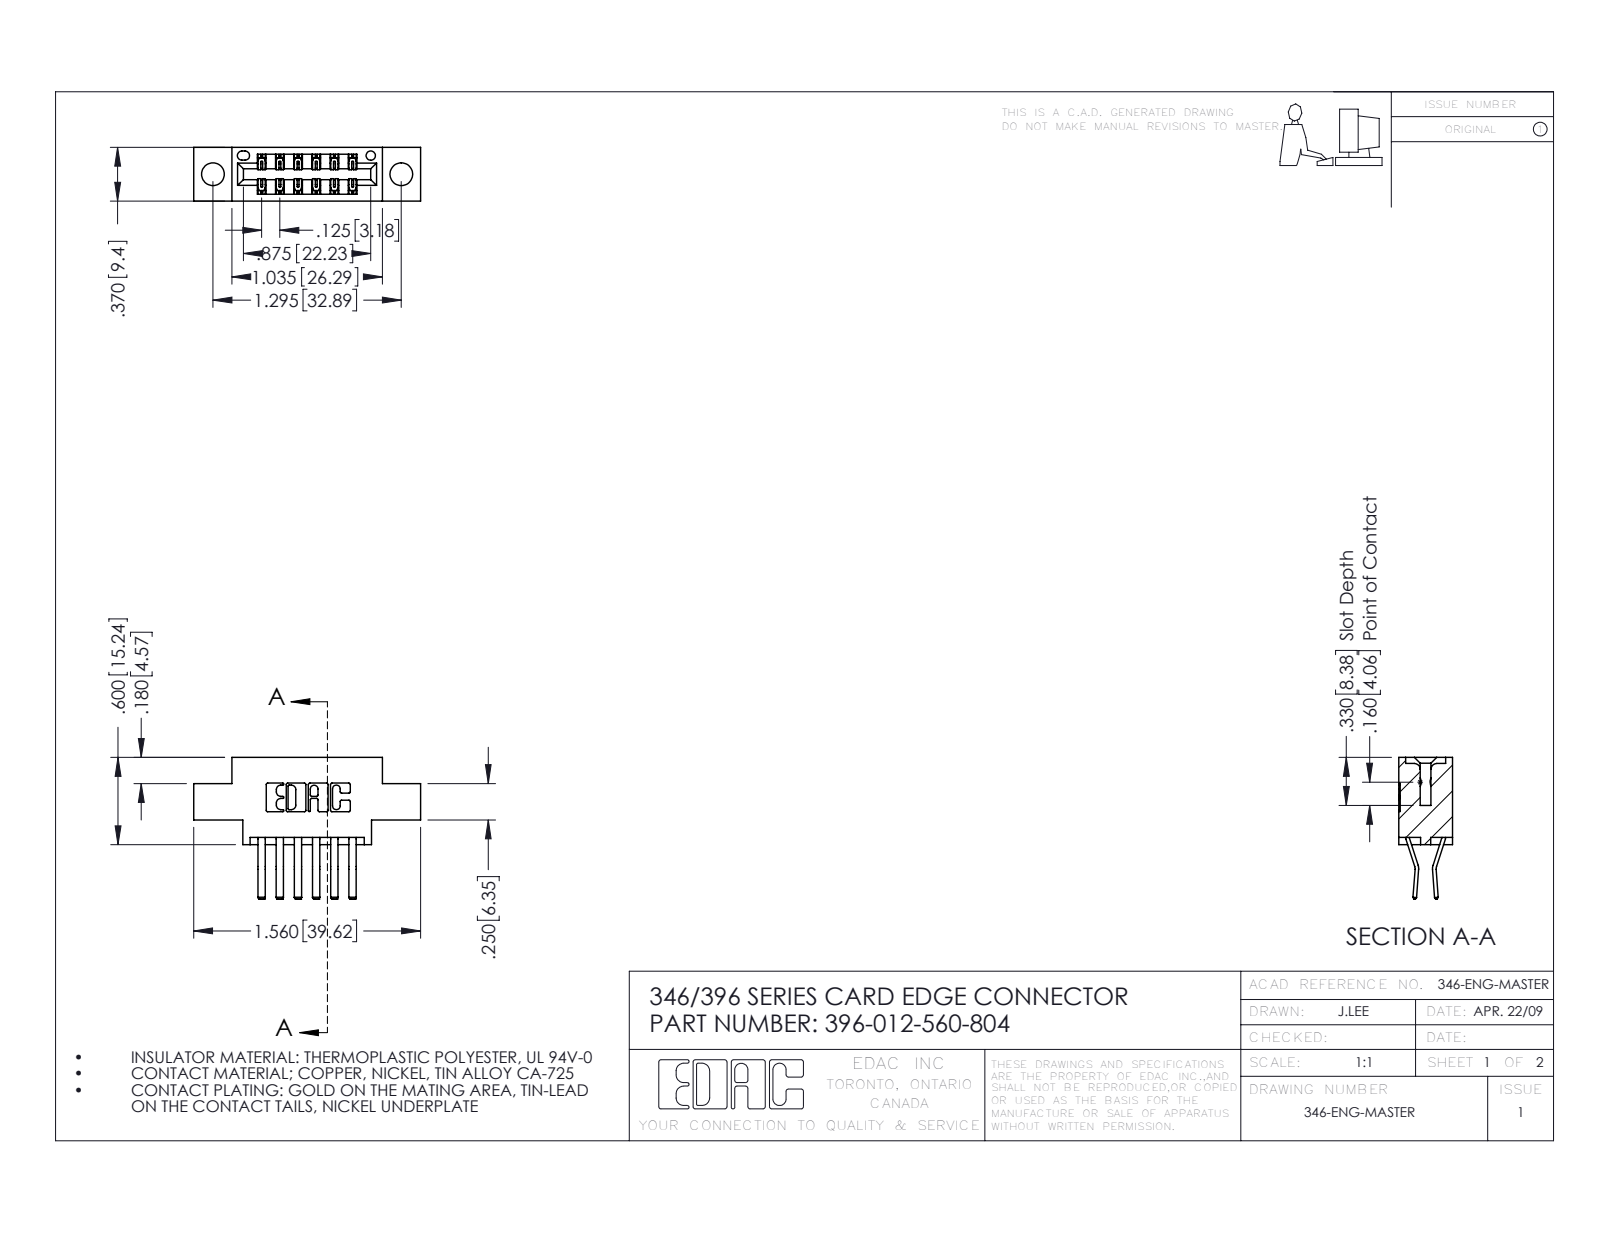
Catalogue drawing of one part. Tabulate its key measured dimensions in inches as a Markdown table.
| quantity | value |
| --- | --- |
| part name | 346 Part_0.170 Offset - 0.156 Dia-TH; 345-292-001_560 Tail; 396-012-560-804 |
| STEP written by | SolidWorks 2016 (CONFIG_CONTROL_DESIGN) |
| units | inches |
| bodies | 13 solids, 774 faces (500 planar, 274 cylindrical, 0 other) |
| overall size | 1.56 × 0.975 × 0.37 |
| volume | 0.209 in³ |
| surface area | 6.725 in² |
| round holes (diameter × count) | 0.156 × 2, 0.064 × 1 |
| partial cylindrical surfaces (radius × count) | 0.01 × 22, 0.006 × 18, 0.007 × 6, 0.031 × 6, 0.026 × 3, 0.01 × 2, 0.014 × 2, 0.022 × 2 |
| main face-to-face distances | 0.25, 0.37, 0.048, 0.322, 0.025, 0.148, 0.222, 0.1, 0.174, 0.072 |
| hole center spacings | 0.246, 1.092, 1.295 |
